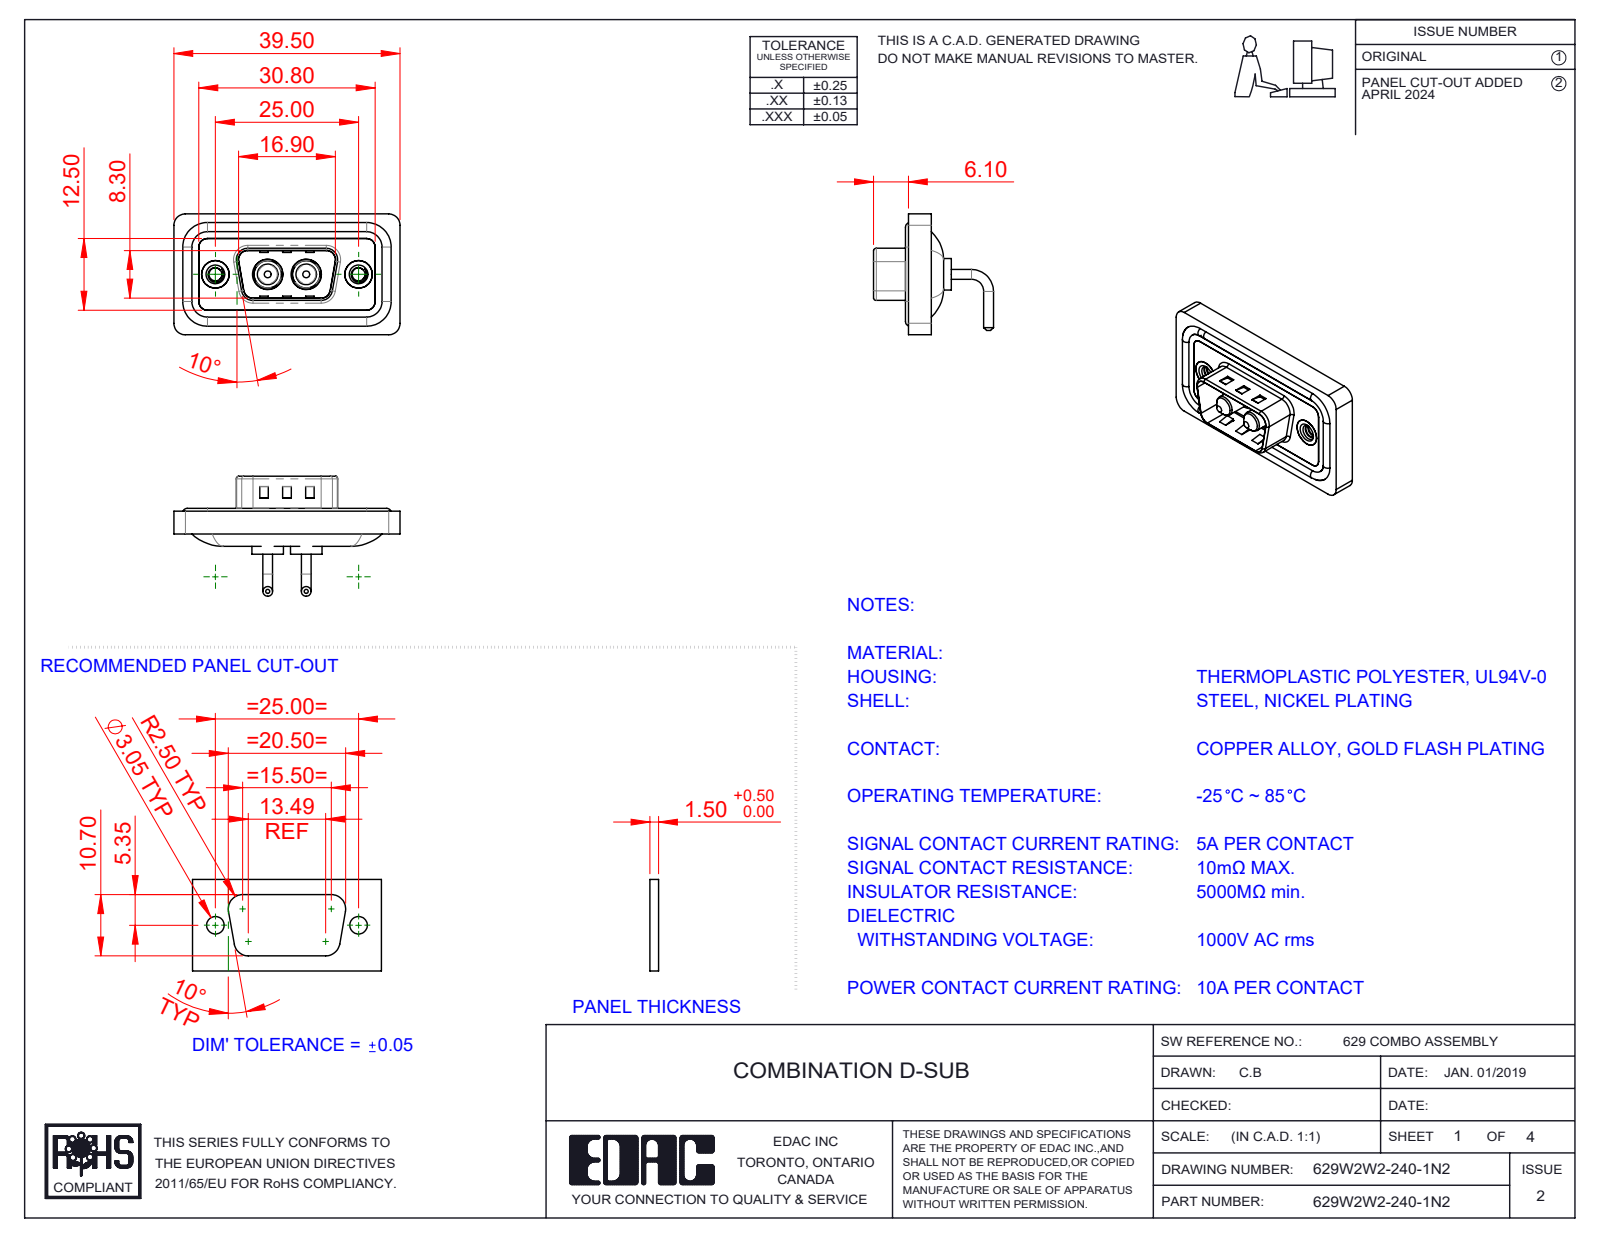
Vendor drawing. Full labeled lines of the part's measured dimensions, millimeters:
Part name (STEP PRODUCT): Power Pin_10A RA; 629Combo Housing_2W2; 629Combo Threaded Rivet_2; 629Combo Shell Rear_09 Contacts (+3 more)
STEP written by: SolidWorks 2023 (CONFIG_CONTROL_DESIGN)
Units: millimetres
Bodies: 11 solids, 497 faces (165 planar, 222 cylindrical, 110 other)
Overall size (bounding box): 39.5 × 21.1 × 20.95
Volume: 4 479 mm³ · Surface area: 7 066 mm²
Round holes (diameter × count): ⌀2.26 ×2, ⌀4 ×2, ⌀4.8 ×2, ⌀4.85 ×2, ⌀5 ×2, ⌀5.3 ×2
Round bosses / shafts (diameter × count): ⌀1.7 ×4, ⌀1.6 ×4, ⌀5.5 ×2, ⌀5.2 ×2, ⌀4.9 ×2, ⌀4.75 ×2, ⌀3.75 ×2, ⌀3.6 ×2
Partial cylindrical surfaces — rounded edges, fillets, slot ends (radius × count): R1.5 ×18, R2 ×18, R0.5 ×8, R1.6 ×8, R0.25 ×4, R0.6 ×4, R0.65 ×4, R0.9 ×4
Main face-to-face distances: 0.4, 2.9, 1.1, 0.8, 2.1, 2.5, 3.1, 1.6, 4.5, 1.5
Hole centre spacings: 9.14, 15.86, 6.72, 25
